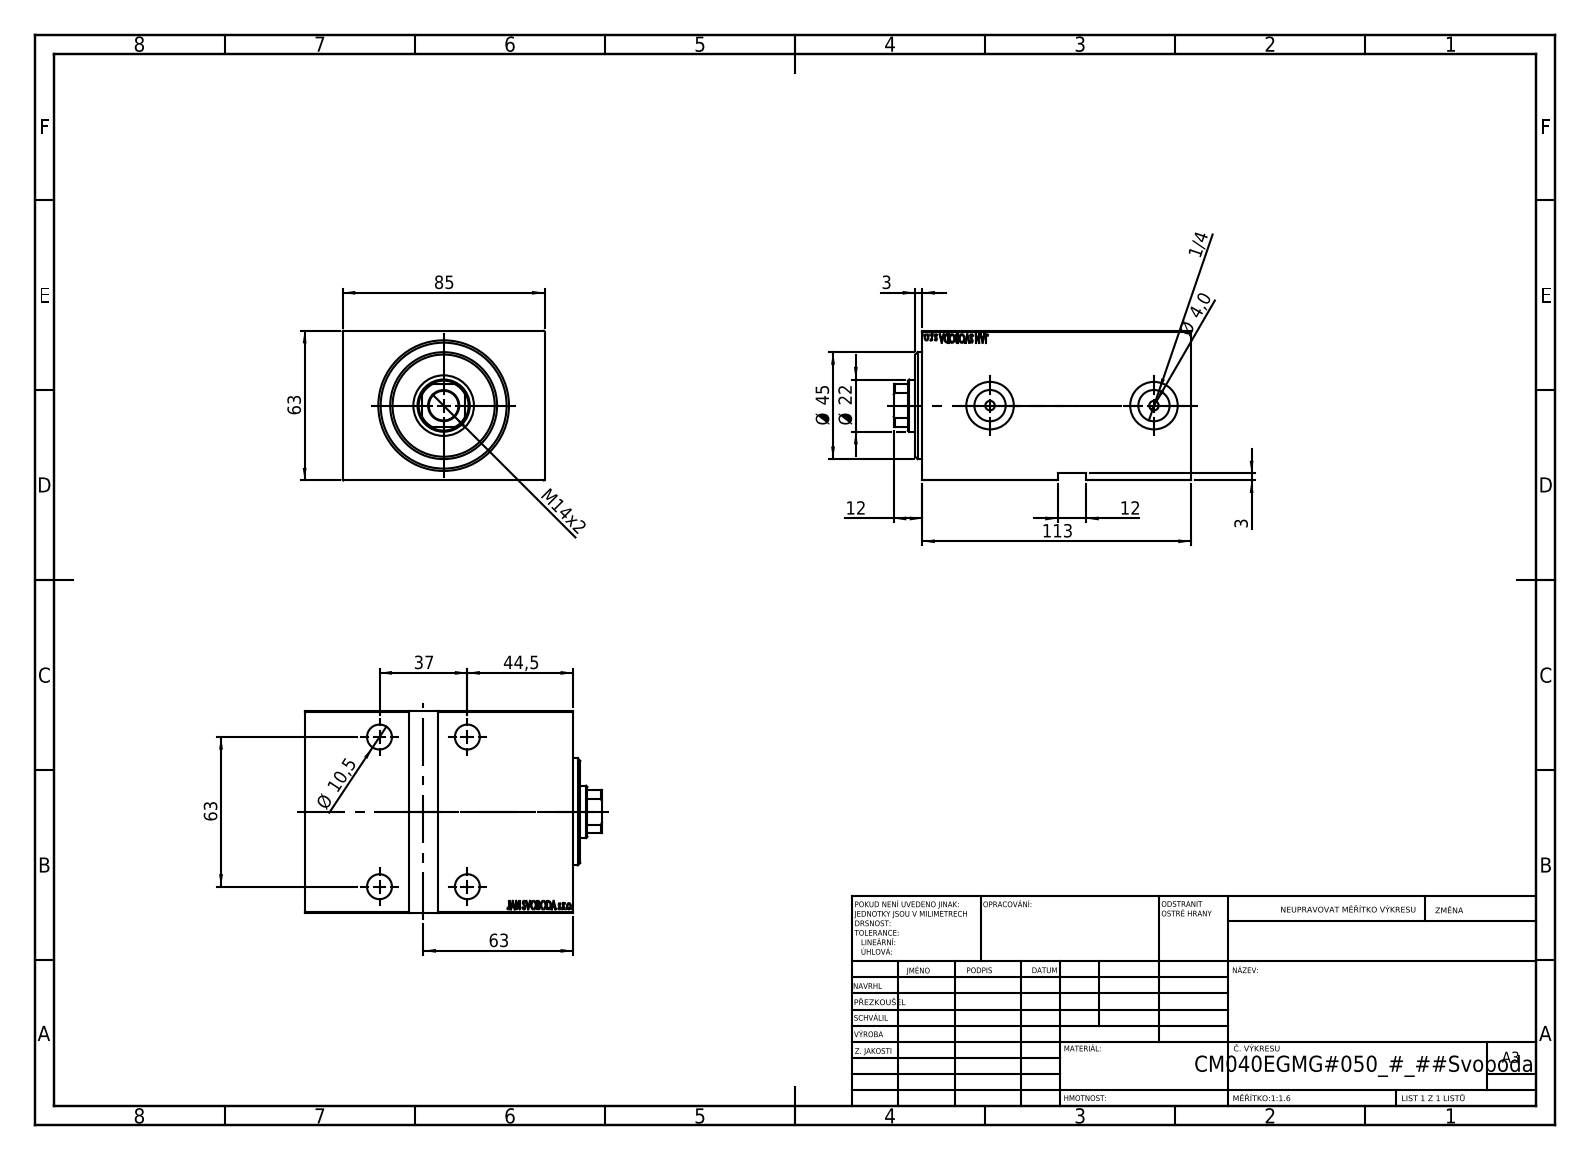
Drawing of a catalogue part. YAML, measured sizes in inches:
part_name: "V450CM_E_Body; V450CM_VC_B; V450CM_E_VCP"
step_written_by: "SolidWorks 2019 (CONFIG_CONTROL_DESIGN)"
units: inches
bodies: {solids: 3, faces: 858, planar: 412, cylindrical: 52, other: 394}
overall_size: [4.921, 3.346, 2.48]
volume: 32.61
surface_area: 137.3
round_holes:
  - {diameter: 0.413, count: 4}
  - {diameter: 0.65, count: 4}
  - {diameter: 0.157, count: 2}
  - {diameter: 0.518, count: 2}
  - {diameter: 0.787, count: 2}
  - {diameter: 0.492, count: 1}
  - {diameter: 0.866, count: 1}
  - {diameter: 1.004, count: 1}
  - {diameter: 1.575, count: 1}
  - {diameter: 2.087, count: 1}
round_bosses_or_shafts:
  - {diameter: 1.772, count: 1}
  - {diameter: 1.654, count: 1}
partial_cylinders:
  - {radius: 0.413, count: 1}
face_to_face_distances: [2.48, 3.346, 4.449, 0.472, 3.976, 0.197, 0.118, 4.252, 3.78, 2.362]
hole_center_spacings: [1.457, 2.48, 2.876, 2.717]
